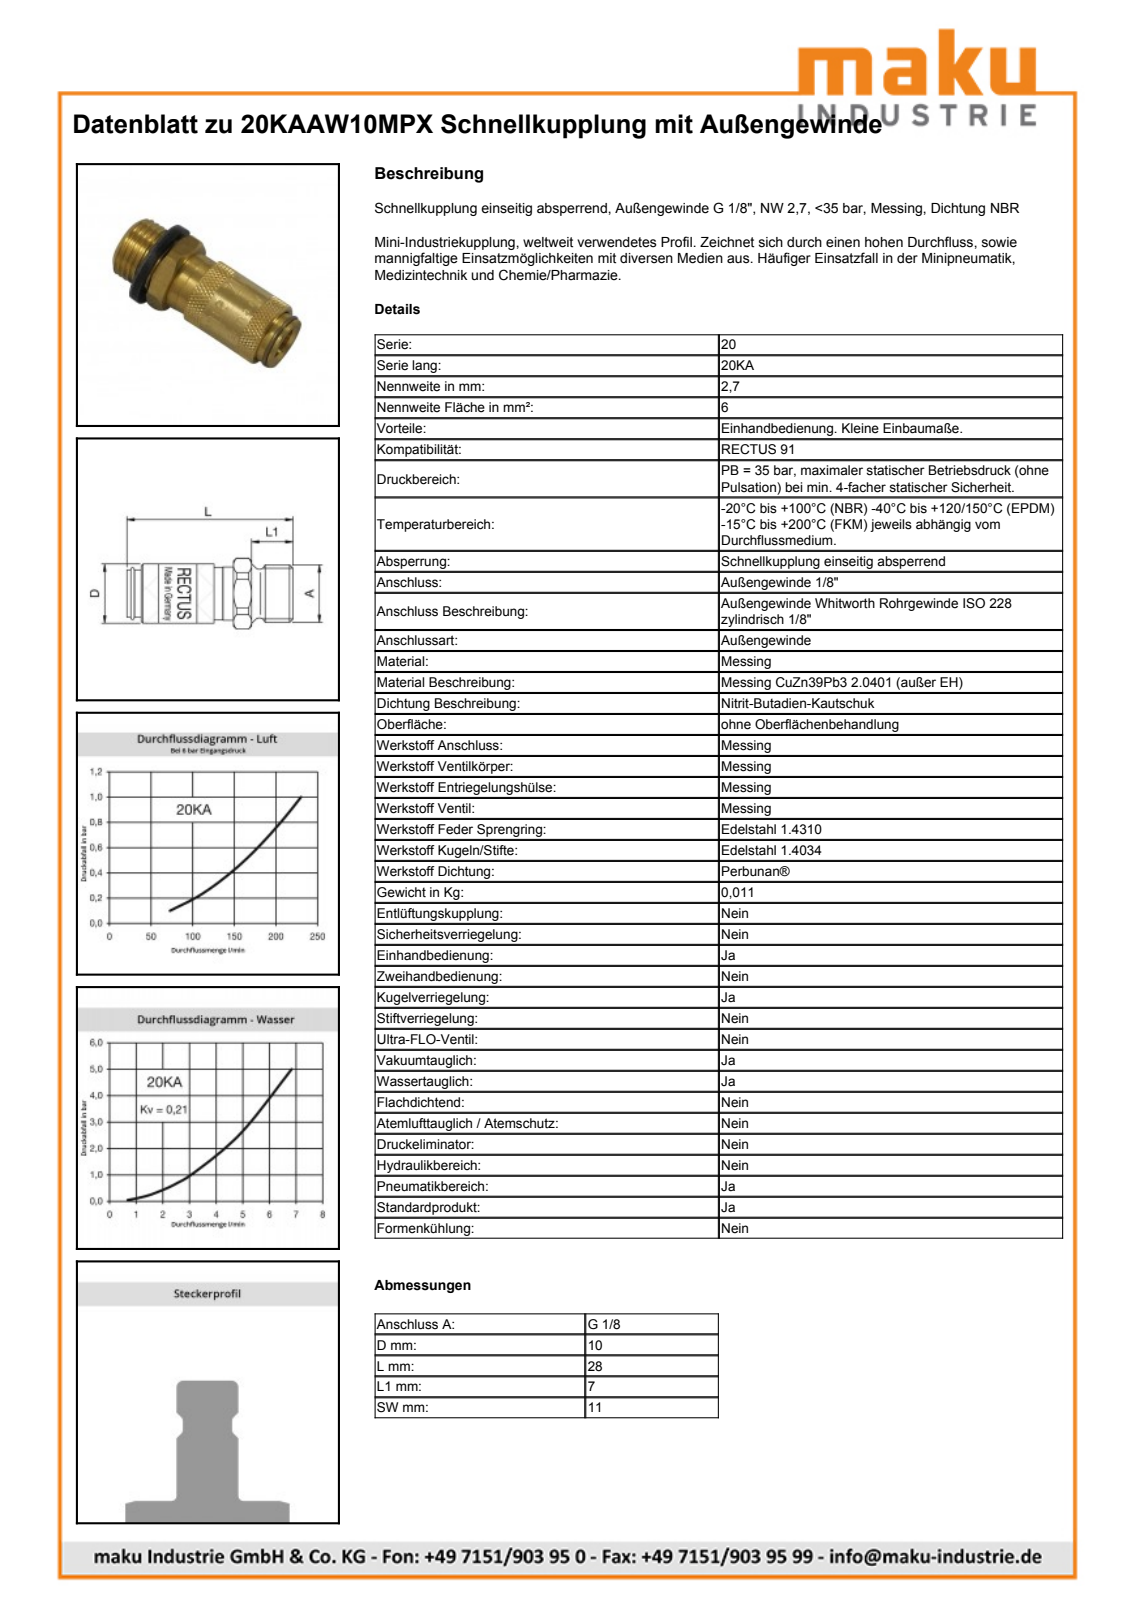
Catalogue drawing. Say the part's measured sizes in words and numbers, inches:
The part is named "D111153". Its 3-D file was written by "Autodesk Inventor 2013 (AUTOMOTIVE_DESIGN)". It is 2 solids with 461 faces: 161 planar, 63 cylindrical and 237 other. Overall it measures 1.104 by 0.512 by 0.512 inches. Its volume is 0.127 cubic inches and its surface area 3.405 square inches. Round holes: 1 of diameter 0.294, 1 of diameter 0.319, 1 of diameter 0.321, 1 of diameter 0.36, 1 of diameter 0.362. Round bosses or shafts: 1 of diameter 0.512, 1 of diameter 0.407, 1 of diameter 0.394, 1 of diameter 0.383, 1 of diameter 0.354, 1 of diameter 0.35, 1 of diameter 0.315, 1 of diameter 0.307. Partial cylindrical surfaces (rounded edges, fillets, slot ends): 1 of radius 0.193, 1 of radius 0.195, 1 of radius 0.236. The main face-to-face distances are 0.217, 0.888, 1.104, 0.396, 0.433, 0.709, 0.179, 0.276, 0.12, 0.829.
